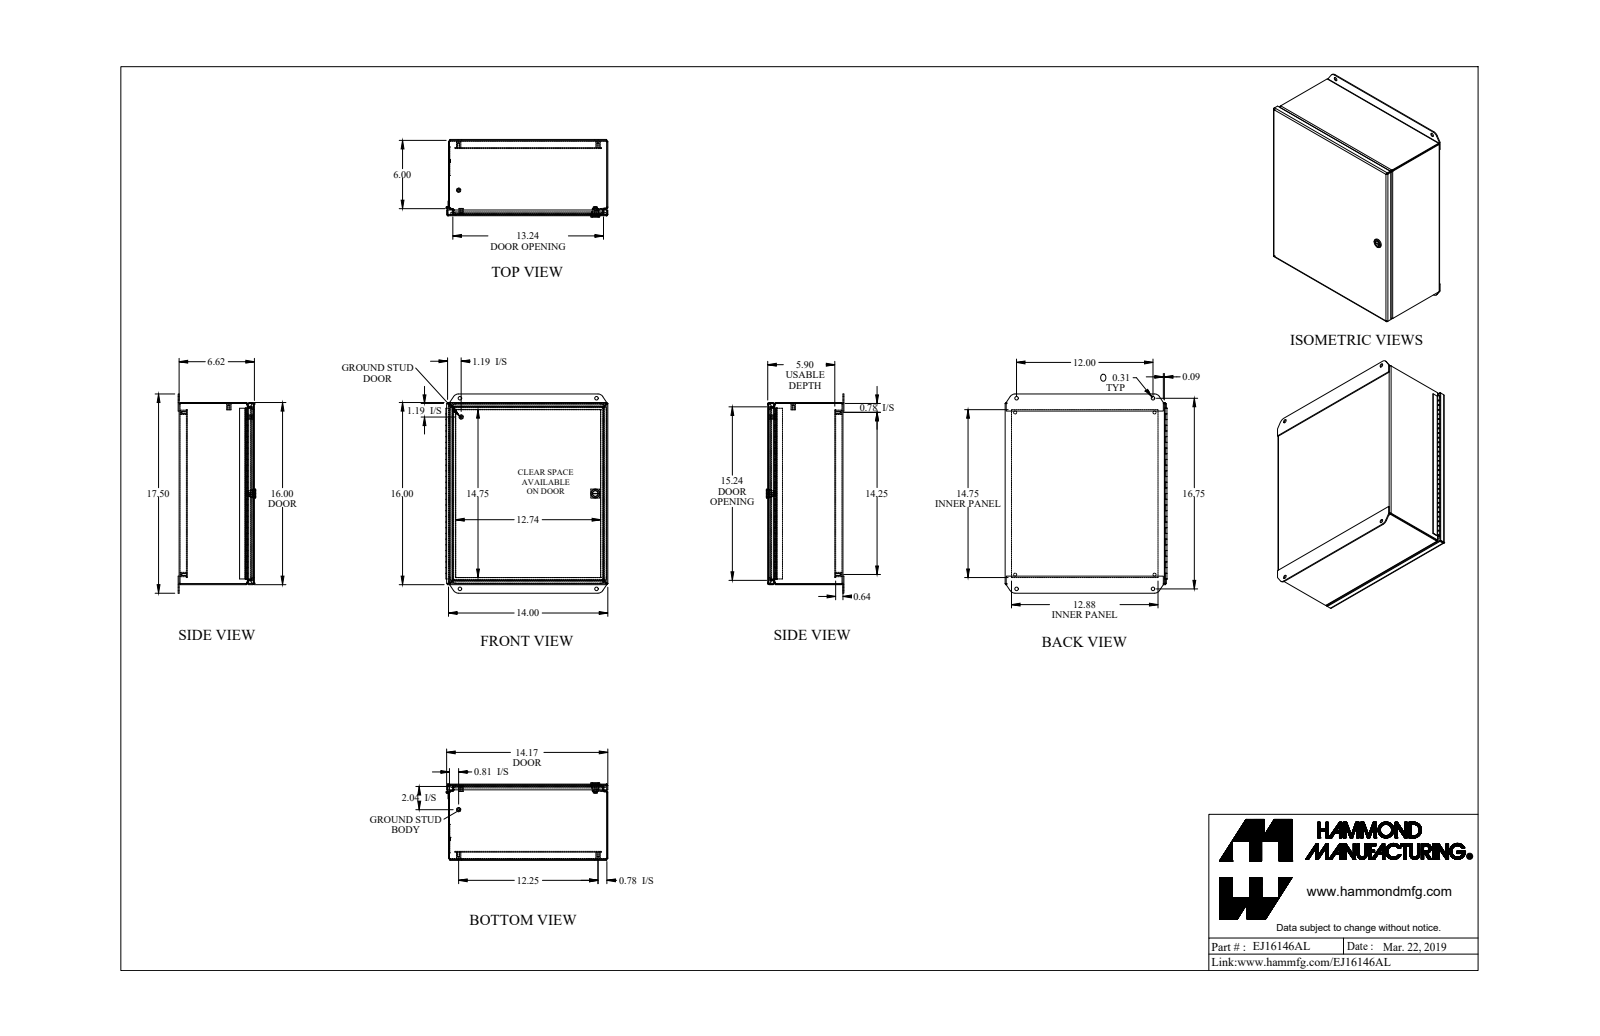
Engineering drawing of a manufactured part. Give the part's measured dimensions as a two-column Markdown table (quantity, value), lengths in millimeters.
| quantity | value |
| --- | --- |
| part name | EJ16146AL_Default |
| STEP written by | SolidWorks 2019 (CONFIG_CONTROL_DESIGN) |
| units | millimeters |
| bodies | 14 solids, 730 faces (500 planar, 162 cylindrical, 68 other) |
| overall size | 444.5 × 361.3 × 173.2 |
| volume | 1 535 000 mm³ |
| surface area | 1 541 000 mm² |
| round holes (diameter × count) | 4 × 6, 6.7 × 4, 8 × 4, 13.1 × 1 |
| round bosses / shafts (diameter × count) | 9.5 × 6, 8.4 × 6, 20 × 1, 13.6 × 1, 12.6 × 1, 11 × 1, 4.6 × 1, 2.5 × 1 |
| partial cylindrical surfaces (radius × count) | 1 × 16, 3.1 × 16, 7.1 × 12, 6.4 × 4, 12.7 × 4, 12.7 × 4, 1.5 × 2, 0.8 × 1 |
| main face-to-face distances | 2.1, 166, 168.1, 164, 353.5, 16.3, 14.3, 151.7, 149.7, 149.9 |
| hole center spacings | 31.9, 309.6, 393.7, 499.8, 0.6, 181.1, 212.8, 304.8 |
